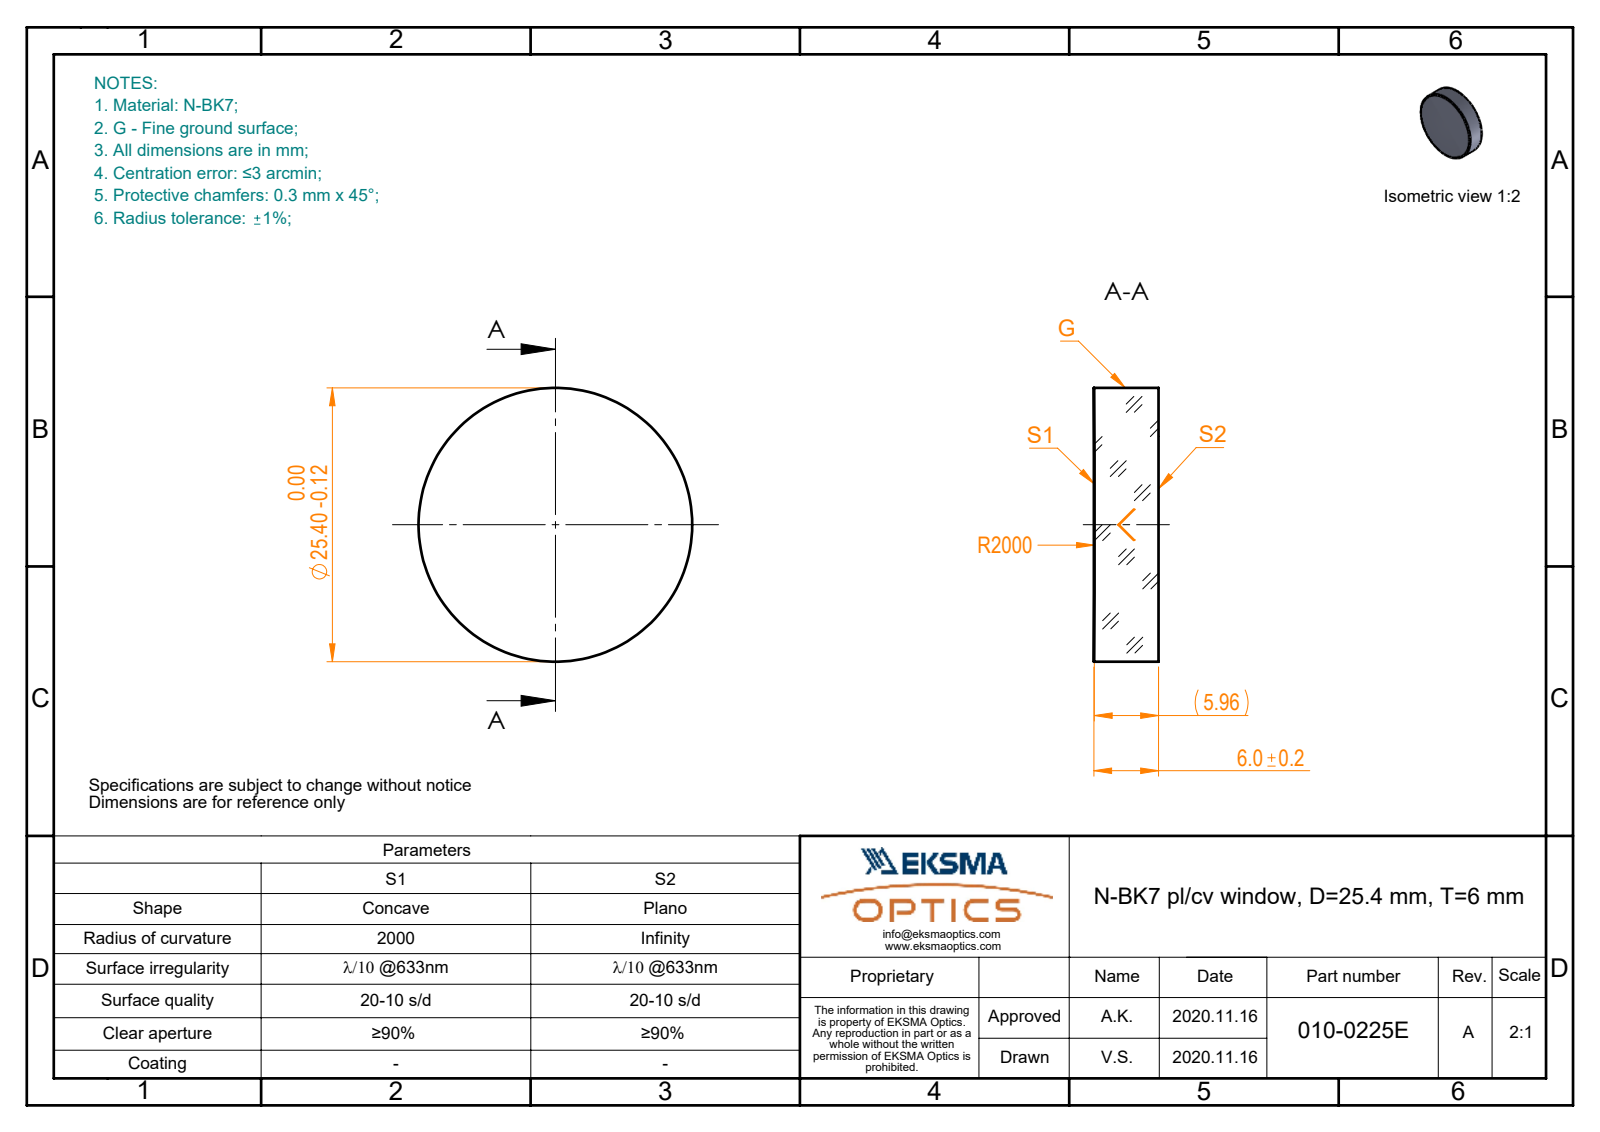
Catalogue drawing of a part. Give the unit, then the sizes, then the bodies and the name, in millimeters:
Units: millimetres
Overall size (bounding box): 25.4 × 25.4 × 6
Round bosses / shafts (diameter × count): ⌀25.4 ×1
Volume: 3 030 mm³ · Surface area: 1 492 mm²
Bodies: 1 solid, 5 faces (1 planar, 2 cylindrical, 2 other)
Part name (STEP PRODUCT): 010-0225E_N-BK7_PCV_window
STEP written by: SolidWorks 2019 (CONFIG_CONTROL_DESIGN)
